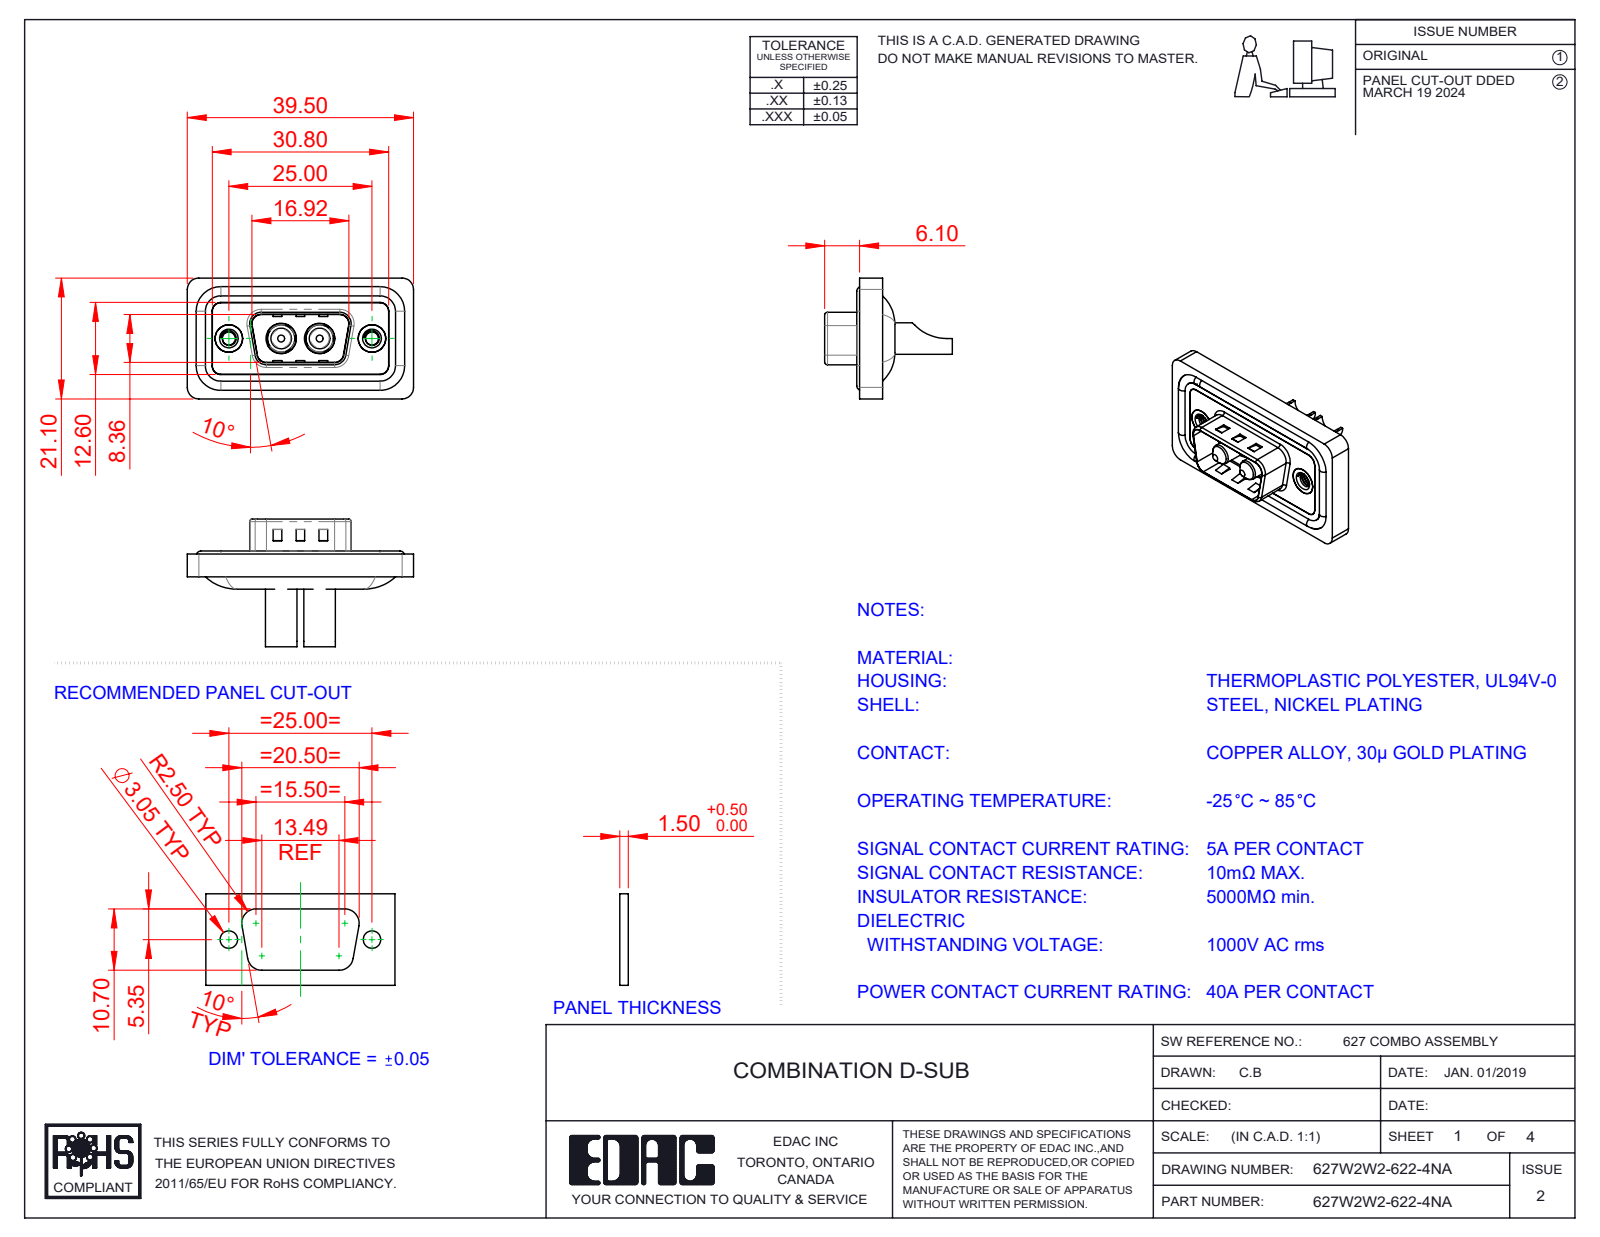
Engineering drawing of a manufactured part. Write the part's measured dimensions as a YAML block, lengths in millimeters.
part_name: "Power Pin_40A SC; 627Combo Shell Front_09 Contacts; 627Combo Waterproof Housing_09 Contacts; 627Combo Threaded Rivet_A (+3 more)"
step_written_by: "SolidWorks 2023 (CONFIG_CONTROL_DESIGN)"
units: millimeters
bodies: {solids: 11, faces: 495, planar: 169, cylindrical: 222, other: 104}
overall_size: [39.5, 22.3, 21.1]
volume: 4542
surface_area: 7261
round_holes:
  - {diameter: 2.26, count: 2}
  - {diameter: 4, count: 2}
  - {diameter: 4.6, count: 2}
  - {diameter: 4.8, count: 2}
  - {diameter: 4.85, count: 2}
  - {diameter: 5, count: 2}
  - {diameter: 5.3, count: 2}
round_bosses_or_shafts:
  - {diameter: 1.6, count: 4}
  - {diameter: 5.5, count: 2}
  - {diameter: 5.2, count: 2}
  - {diameter: 4.9, count: 2}
  - {diameter: 4.75, count: 2}
  - {diameter: 3.75, count: 2}
  - {diameter: 3.6, count: 2}
partial_cylinders:
  - {radius: 1.5, count: 22}
  - {radius: 2, count: 18}
  - {radius: 0.5, count: 8}
  - {radius: 1.6, count: 8}
  - {radius: 0.25, count: 4}
  - {radius: 0.6, count: 4}
  - {radius: 0.65, count: 4}
  - {radius: 0.9, count: 4}
face_to_face_distances: [0.4, 1.1, 2.9, 3.1, 0.5, 1.6, 1.5, 2.5, 0.7, 4]
hole_center_spacings: [9.14, 15.86, 6.72, 25]
